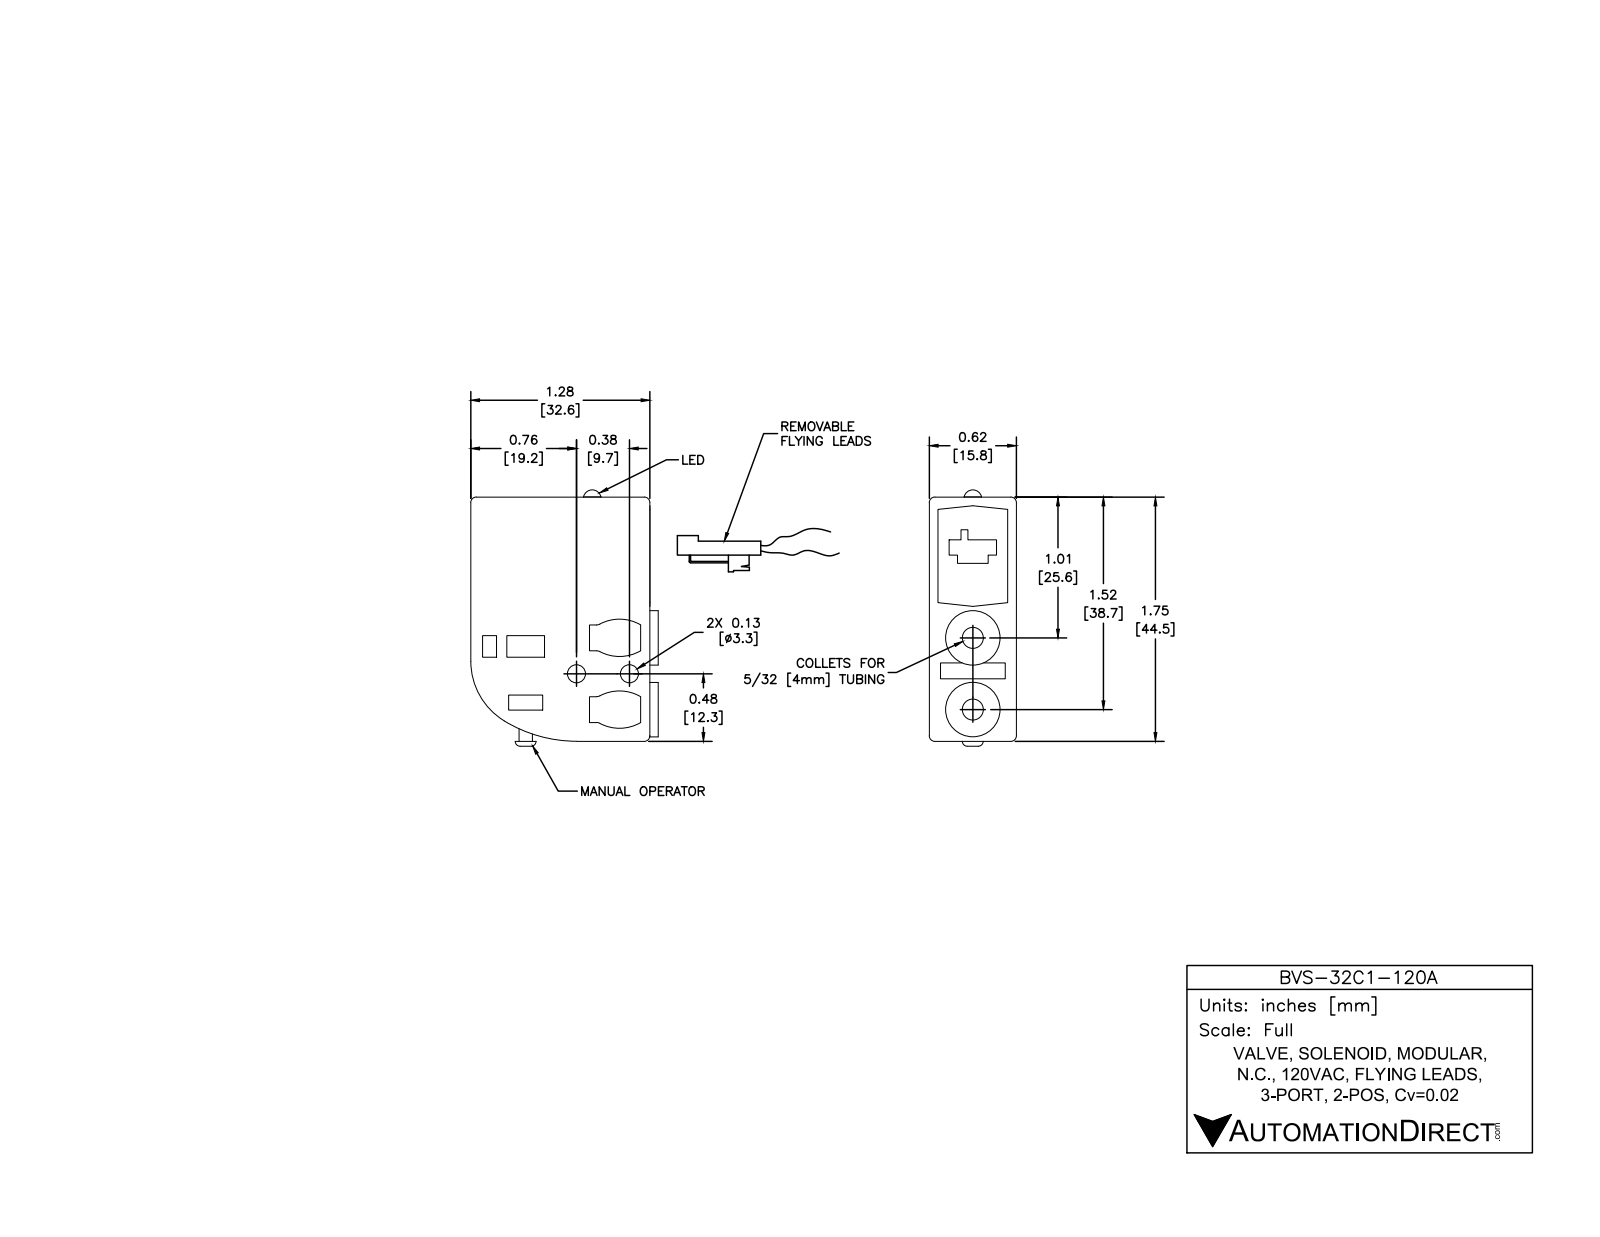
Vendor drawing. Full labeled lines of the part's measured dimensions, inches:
Part name (STEP PRODUCT): BVS-32C1-120A
STEP written by: SolidWorks 2013 (AUTOMOTIVE_DESIGN)
Units: inches
Bodies: 1 solid, 158 faces (93 planar, 52 cylindrical, 13 other)
Overall size (bounding box): 1.836 × 1.347 × 0.624
Volume: 1.246 in³ · Surface area: 10.17 in²
Round holes (diameter × count): ⌀0.13 ×2, ⌀0.15 ×2, ⌀0.254 ×2, ⌀0.046 ×1
Round bosses / shafts (diameter × count): ⌀0.39 ×2, ⌀0.124 ×1, ⌀0.096 ×1
Partial cylindrical surfaces — rounded edges, fillets, slot ends (radius × count): R0.04 ×11, R0.05 ×4, R0.3 ×4, R0.5 ×1, R1 ×1
Main face-to-face distances: 0.624, 0.1, 0.524, 1.287, 1.288, 1.75, 0.424, 0.06, 0.059, 1.347
Hole centre spacings: 0.061, 0.38, 0.453, 0.514
